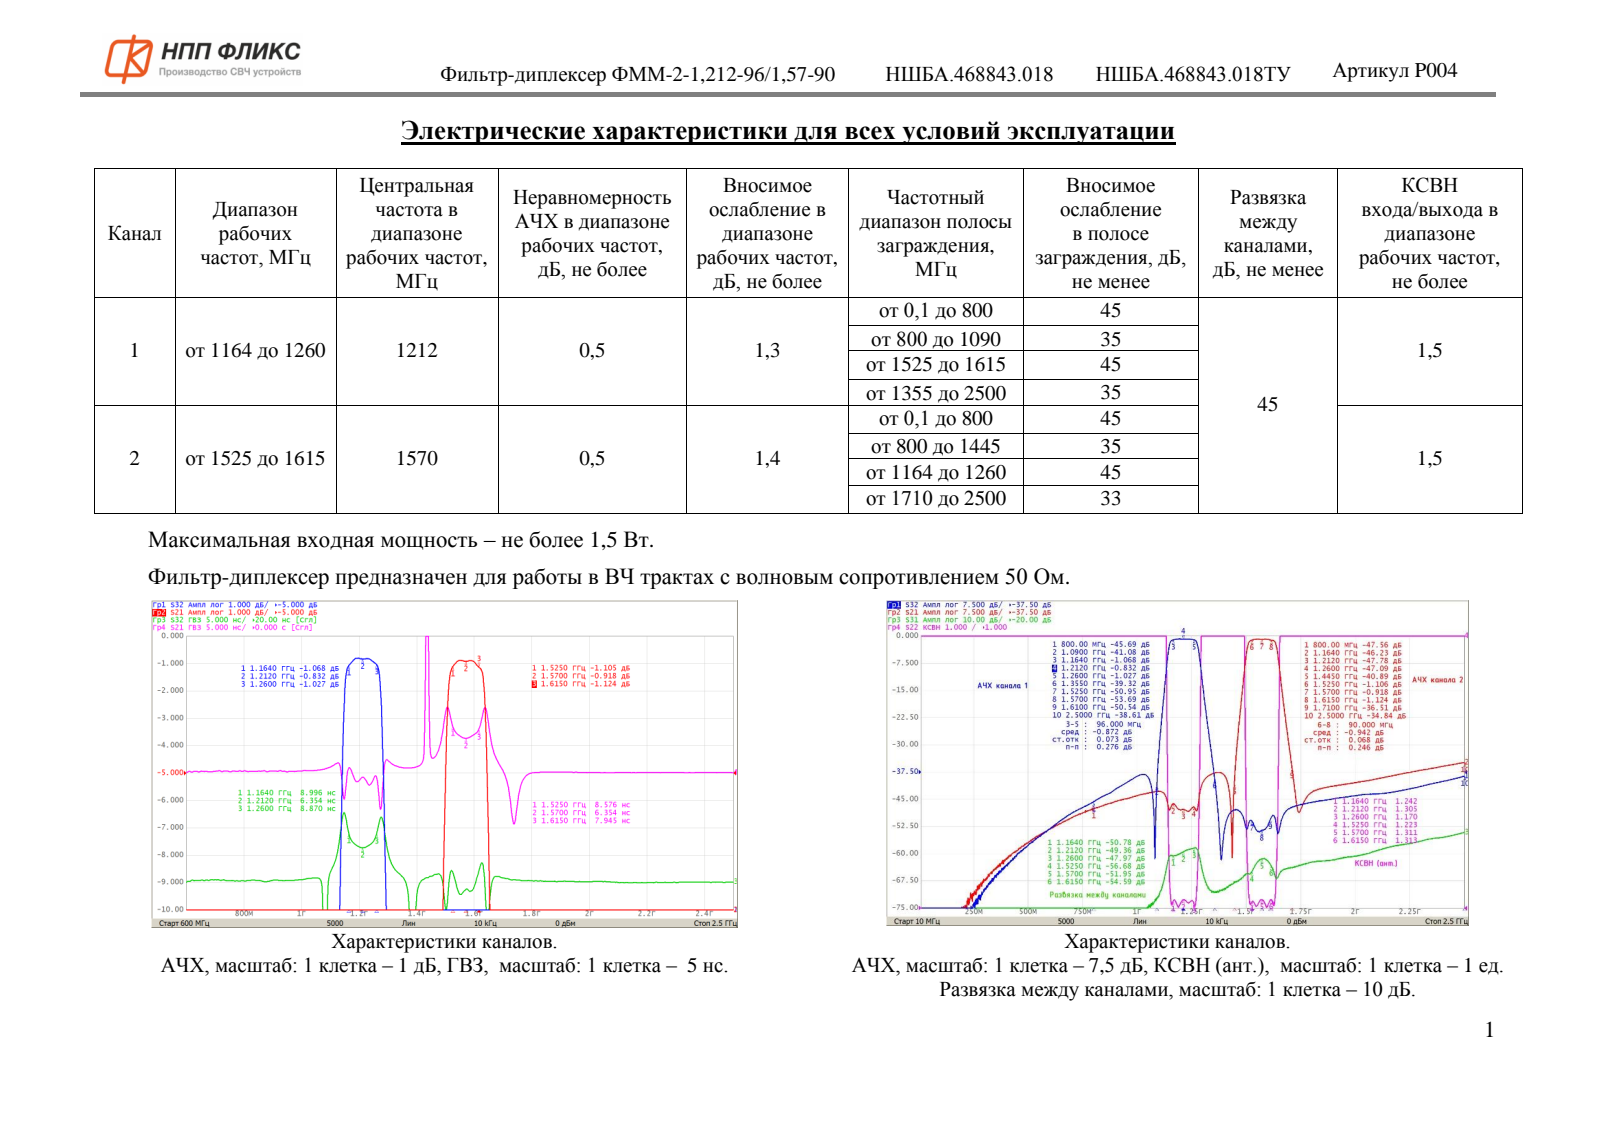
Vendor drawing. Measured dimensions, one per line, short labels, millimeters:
name: НШБА.468843.018_Диплексер ФММ-2-1,212-96(1,57-90
written by: ASCON Math Kernel (CONFIG_CONTROL_DESIGN)
unit: mm
bodies: 1 solid, 949 faces (822 planar, 38 cylindrical, 89 other)
size: 18 × 9.85 × 4.3
volume: 568 mm³; area: 651 mm²
rounds: 23× R0.5, 3× R0.24, 1× R0.12, 1× R0.3, 1× R0.36, 1× R0.42, 1× R0.6
face distances: 4.3, 1.79, 1.49, 1.91, 7.94, 9.85, 7.64, 9.55, 6.15, 8.06
